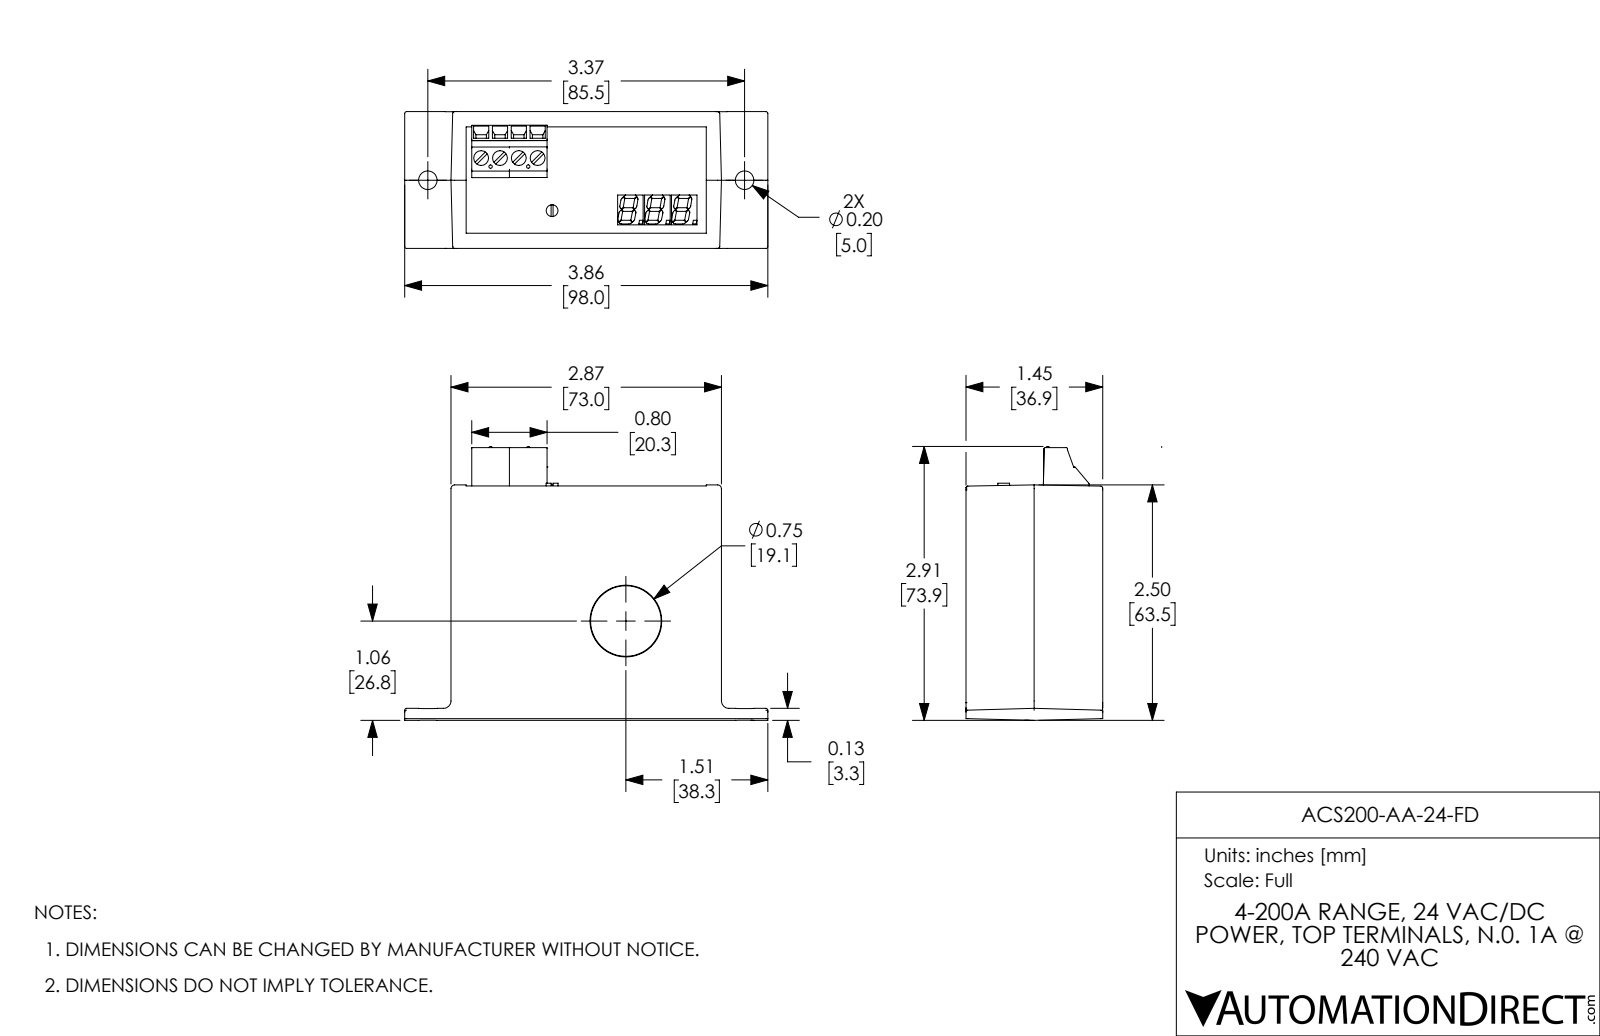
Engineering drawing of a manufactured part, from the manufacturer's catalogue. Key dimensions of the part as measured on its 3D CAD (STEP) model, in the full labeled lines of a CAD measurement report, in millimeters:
Part name (STEP PRODUCT): ACS200-AA-24-FD
STEP written by: SolidWorks 2017 (AUTOMOTIVE_DESIGN)
Units: millimetres
Bodies: 1 solid, 461 faces (308 planar, 74 cylindrical, 79 other)
Overall size (bounding box): 98 × 73.9 × 36.9
Volume: 157 800 mm³ · Surface area: 24 780 mm²
Round holes (diameter × count): ⌀1.5 ×4, ⌀4 ×4, ⌀5 ×2, ⌀19.1 ×1
Round bosses / shafts (diameter × count): ⌀3.2 ×1
Partial cylindrical surfaces — rounded edges, fillets, slot ends (radius × count): R0.5 ×16, R0.3 ×12, R1 ×4, R2 ×4
Main face-to-face distances: 36.9, 73, 3.3, 1.2, 4.1, 2.8, 34.1, 32.8, 1.3, 30
Hole centre spacings: 5.1, 10.2, 60.6, 101.2, 15.2, 15.6, 20.4, 25.3
